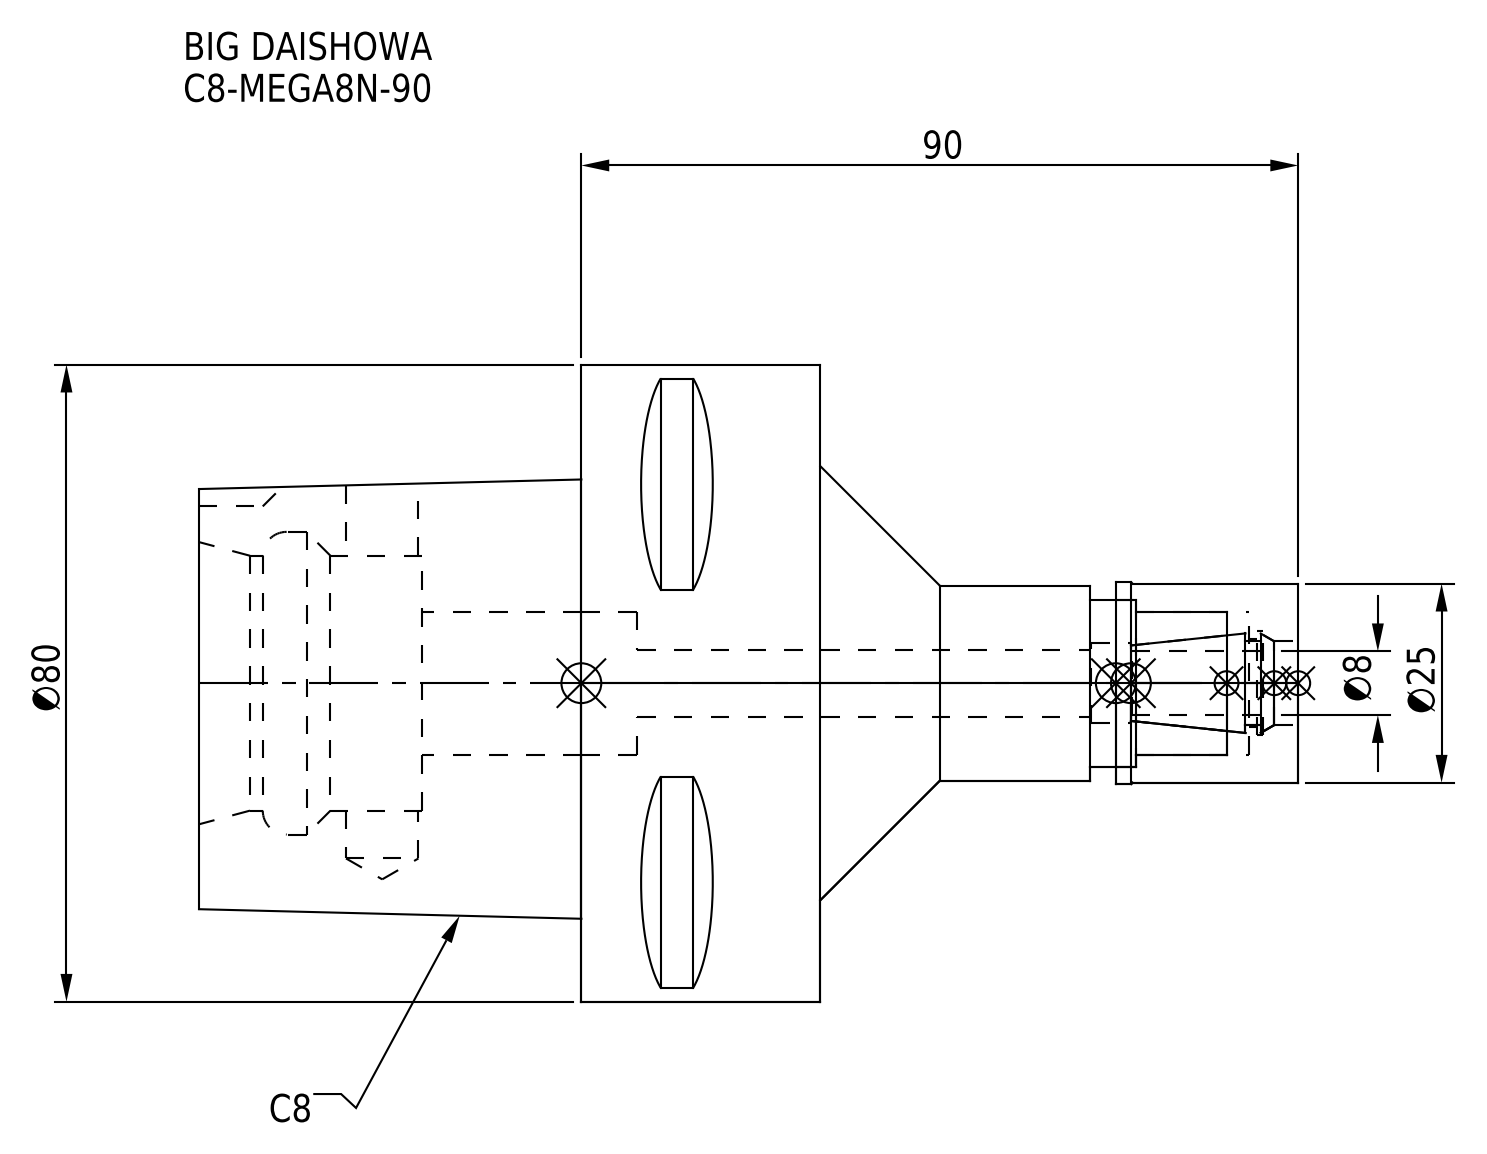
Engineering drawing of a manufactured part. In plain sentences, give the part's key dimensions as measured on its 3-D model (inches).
The part is named "DXF_TEMP_ASSY_ASM_4_ASM.stp; C8-MEGA8N-90_1.stp; C8-MEGA8N-90; C8-MEGA8N-90-080_ASM.stp (+3 more)". Its 3-D file was written by "SolidWorks 2019 (CONFIG_CONTROL_DESIGN)". It is 2 solids with 95 faces: 38 planar, 39 cylindrical and 18 other. Overall it measures 5.433 by 3.15 by 3.15 inches. Its volume is 15.73 cubic inches and its surface area 62.11 square inches. Round holes: 1 of diameter 0.331, 1 of diameter 0.358, 1 of diameter 0.394, 1 of diameter 0.413, 1 of diameter 0.433, 1 of diameter 0.512, 1 of diameter 0.709, 1 of diameter 0.827, 1 of diameter 1.26, 1 of diameter 1.496. Round bosses or shafts: 1 of diameter 3.15, 1 of diameter 0.996, 1 of diameter 0.984, 1 of diameter 0.965. Partial cylindrical surfaces (rounded edges, fillets, slot ends): 1 of radius 0.236. The main face-to-face distances are 1.181, 3.071, 1.89, 0.787, 1.969, 1.102, 1.281, 2.362, 3.543, 4.331.
